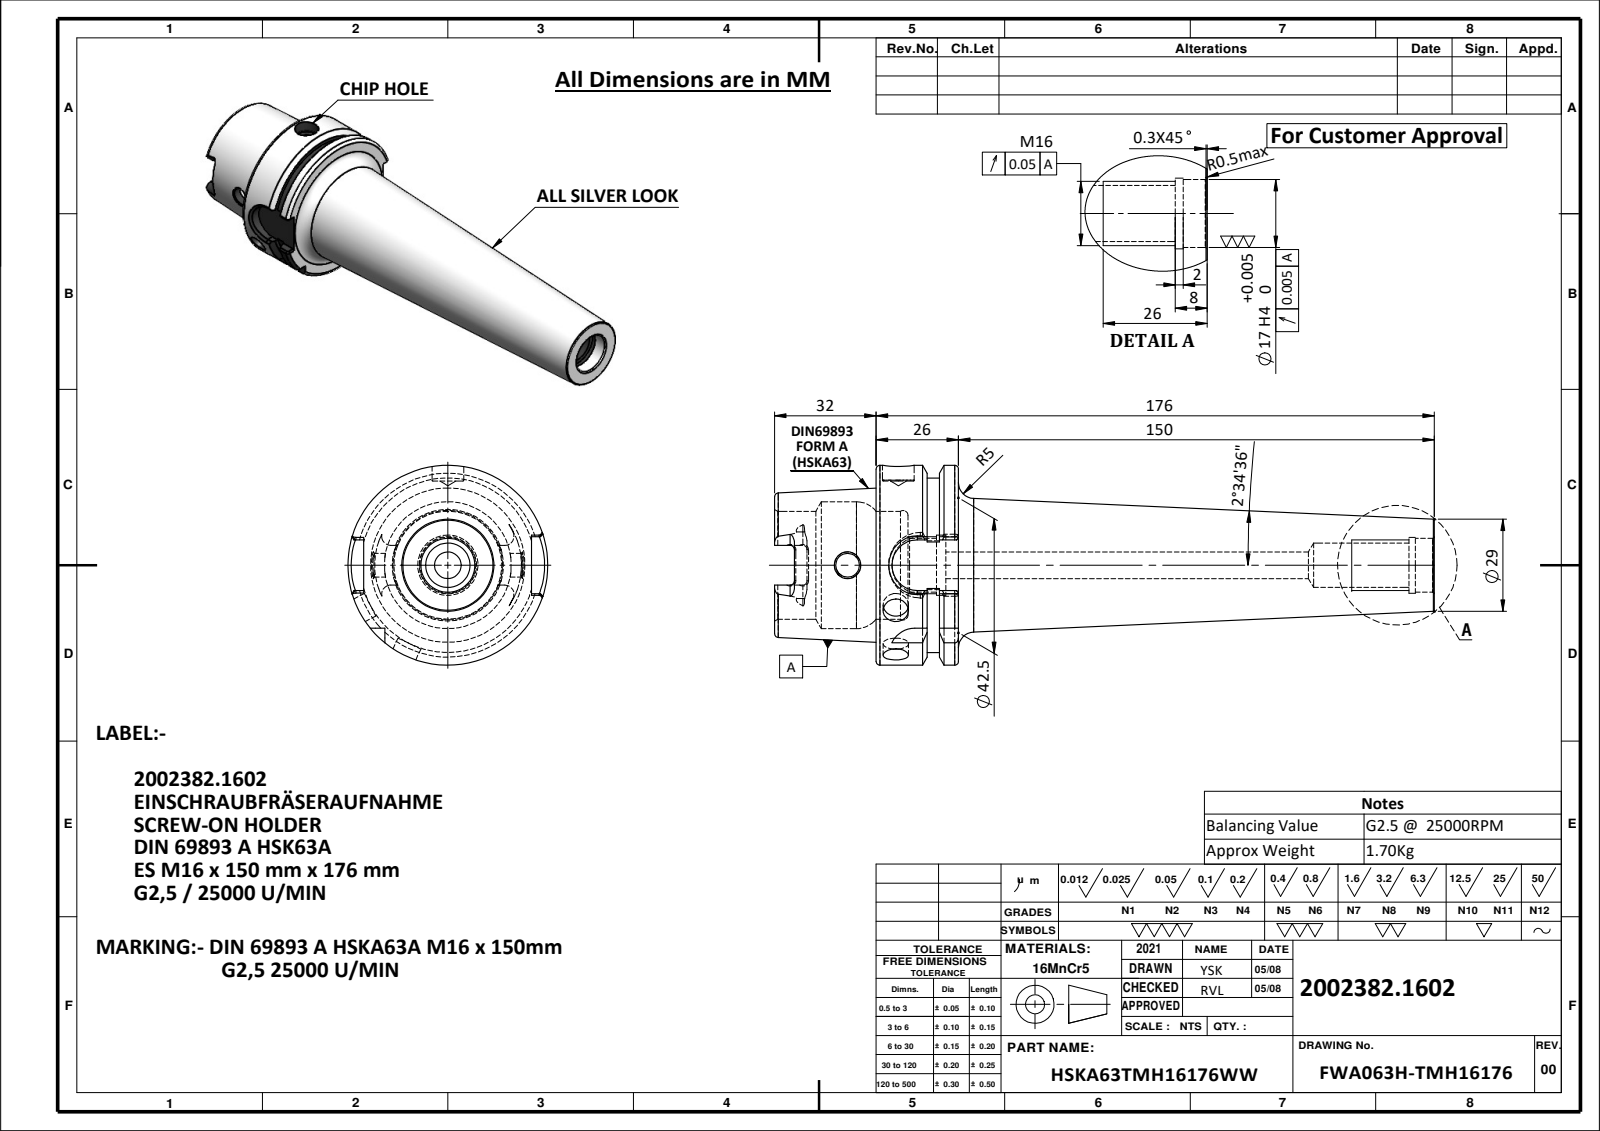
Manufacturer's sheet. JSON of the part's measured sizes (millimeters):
{"part_name": "HSKA63TMS16176WW; FWA063H-TMH16176", "step_written_by": "SolidWorks 2024 (CONFIG_CONTROL_DESIGN)", "units": "millimeters", "bodies": {"solids": 1, "faces": 168, "planar": 51, "cylindrical": 51, "other": 66}, "overall_size": [207.95, 63, 63], "volume_mm3": 221087, "surface_area_mm2": 42881, "round_holes": [[8, 2], [7.5, 1], [8.4, 1], [10, 1], [14, 1], [17, 1], [17.6, 1], [19, 1], [34, 1], [40, 1]], "round_bosses_or_shafts": [[63, 1], [55, 1]], "partial_cylinders_radius": [[1.3, 6], [2.88, 4], [8, 2], [9, 1]], "face_to_face_distances": [25.95, 10, 15.95, 32, 42, 57.95, 207.95, 175.95, 165.95, 150]}
